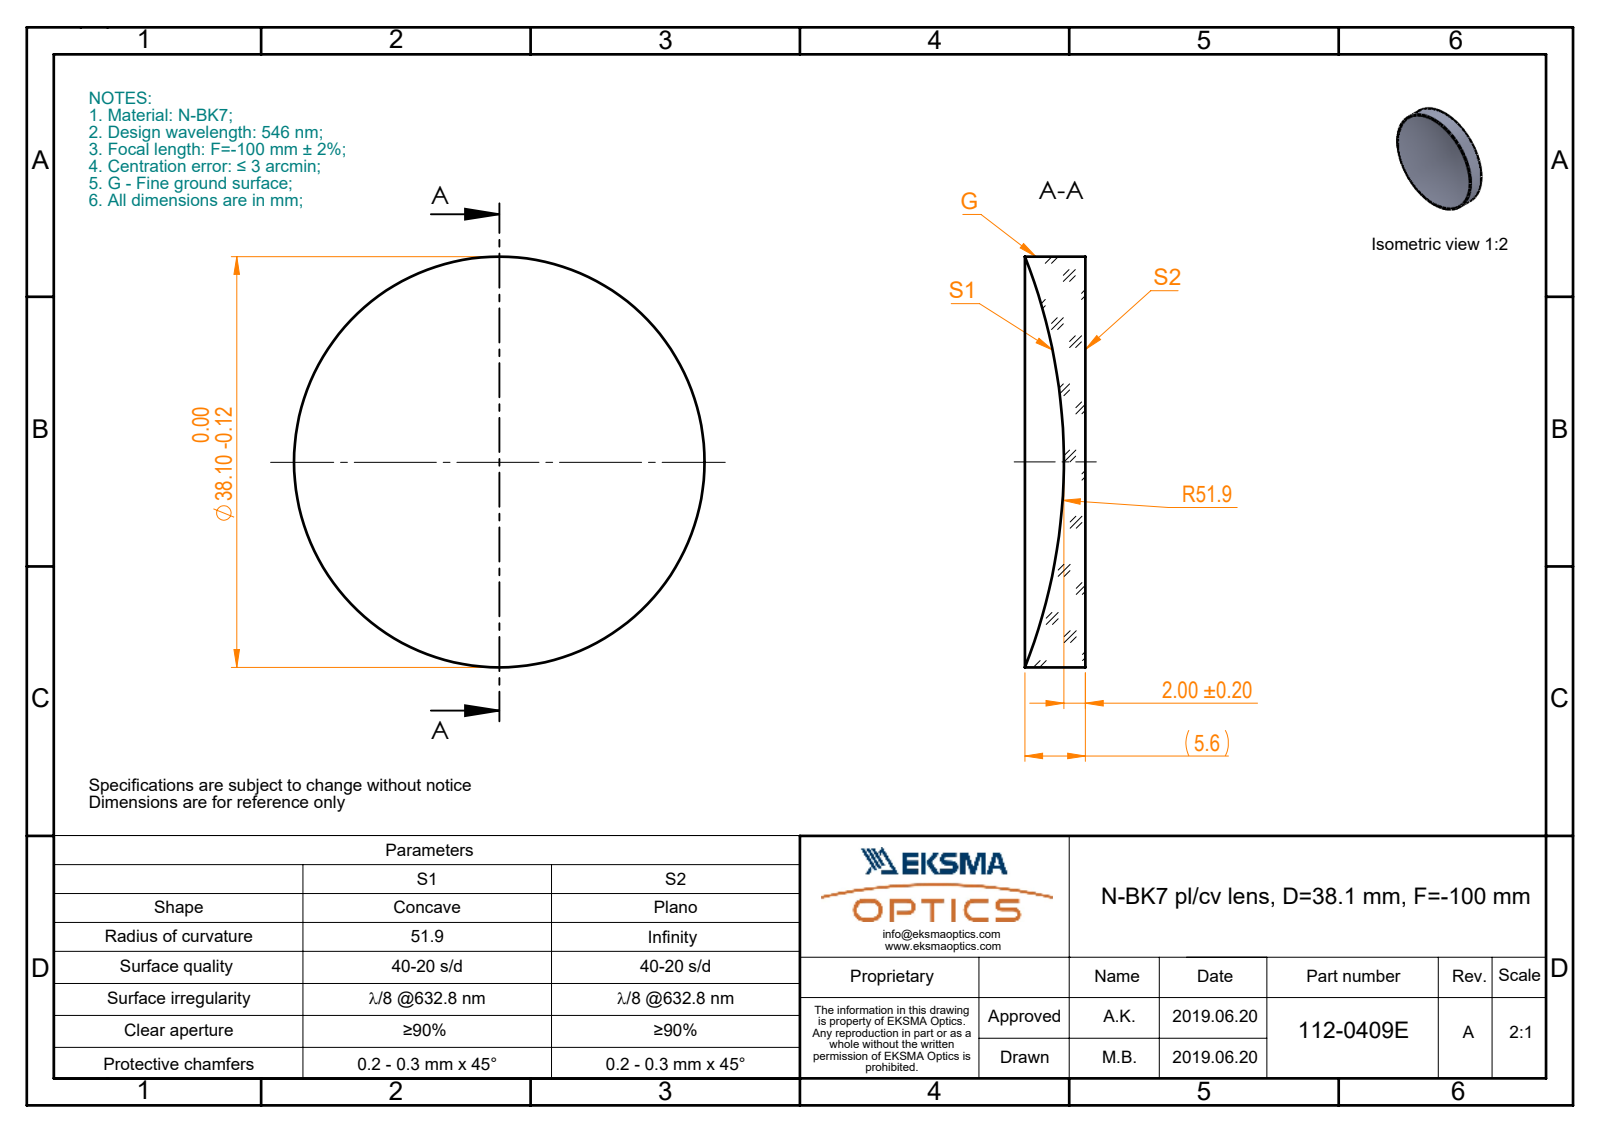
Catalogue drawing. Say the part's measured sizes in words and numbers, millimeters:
The part is named "112-0409E BK7 pl-cv 38.1 F-100". Its 3-D file was written by "SolidWorks 2017 (CONFIG_CONTROL_DESIGN)". It is 1 solid with 5 faces: 1 planar, 2 cylindrical and 2 other. Overall it measures 38.1 by 38.1 by 5.62 millimeters. Its volume is 4 320 cubic millimeters and its surface area 2 994 square millimeters. Round bosses or shafts: 1 of diameter 38.1.
